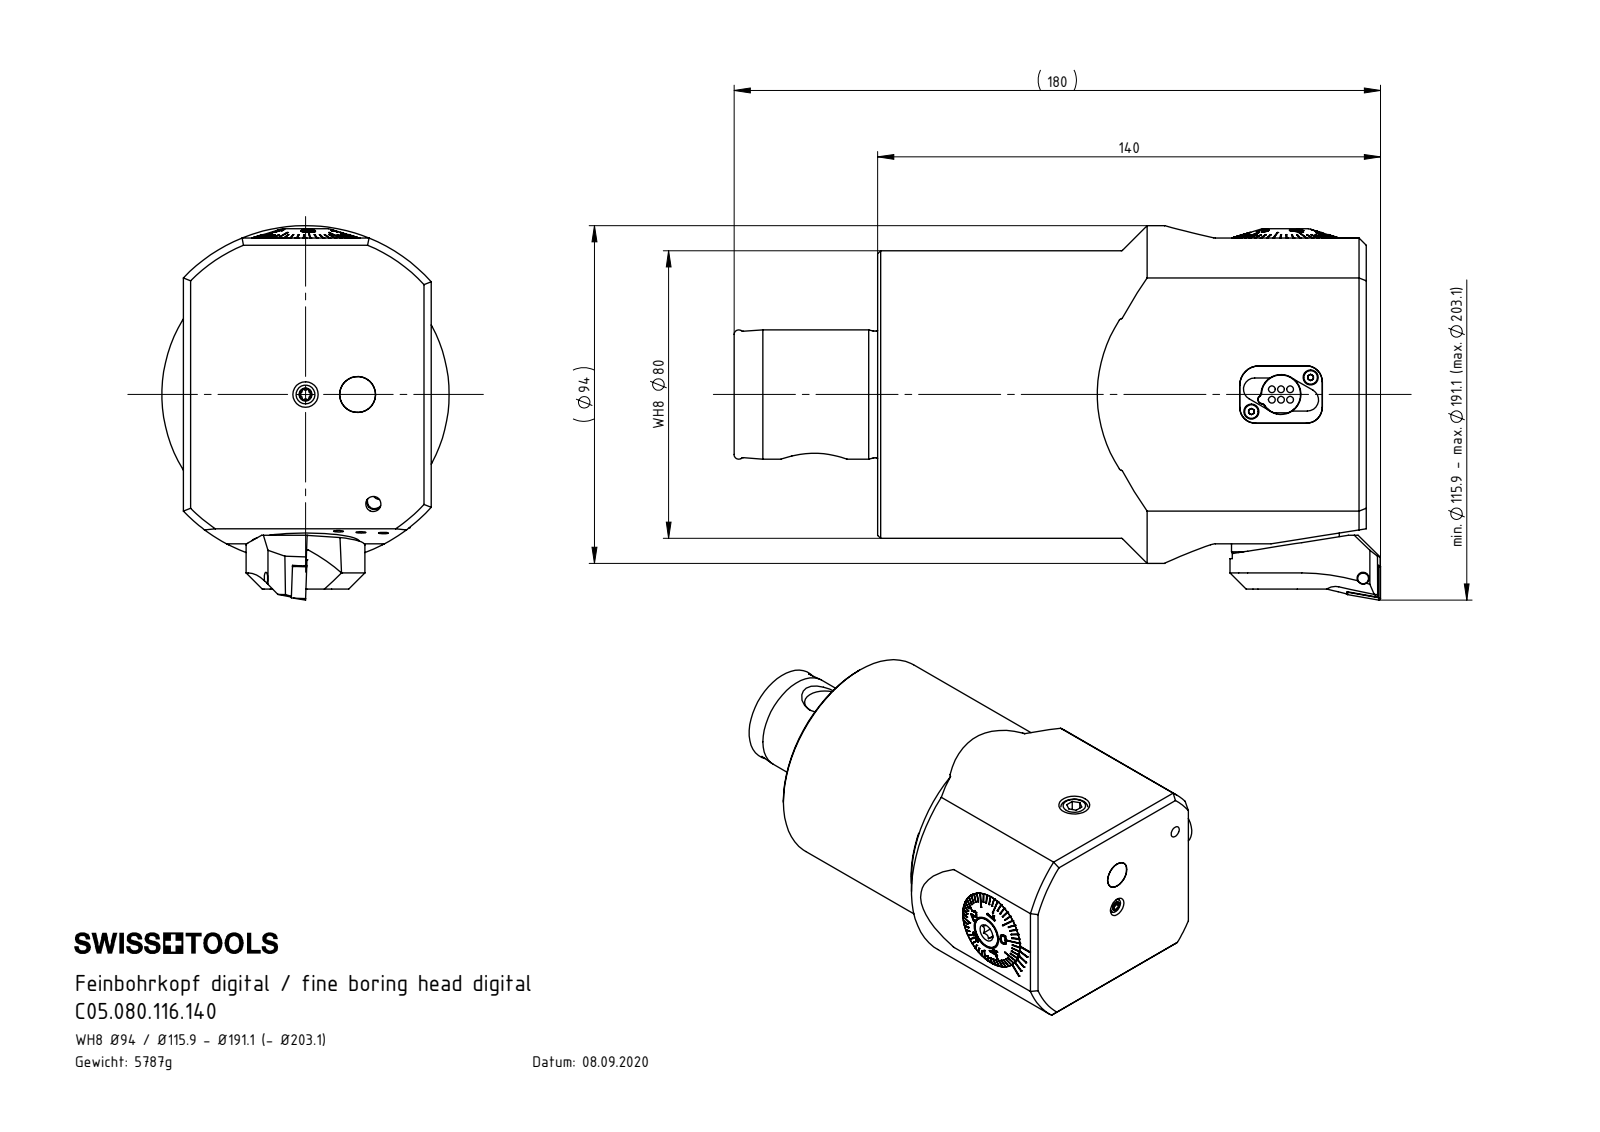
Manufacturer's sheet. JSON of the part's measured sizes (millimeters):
{"part_name": "Fxx-BG7.DA1.0xx_B_F72; WCB-ER2.001.009_A; Klebstoff D10; ISO 4026 - M10 x 16 (+8 more)", "step_written_by": "SolidWorks 2017 (CONFIG_CONTROL_DESIGN)", "units": "millimeters", "bodies": {"solids": 31, "faces": 1006, "planar": 469, "cylindrical": 219, "other": 318}, "overall_size": [176, 101.15, 80], "volume_mm3": 740095, "surface_area_mm2": 91312, "round_holes": [[4.2, 5], [2.5, 3], [1.6, 2], [2.2, 2], [3.3, 2], [8.5, 2], [13, 2], [5, 1], [8, 1], [9.5, 1], [10, 1], [10.2, 1]], "round_bosses_or_shafts": [[1.9, 6], [10, 2], [3.8, 2], [2, 2], [80, 1], [36, 1], [35.3, 1], [30, 1]], "partial_cylinders_radius": [[0.34, 6], [0.59, 6], [1.1, 6], [1.2, 6], [2, 6], [2.5, 6], [3.2, 3], [4.4, 3]], "face_to_face_distances": [69, 136, 6.5, 40, 176, 78.6, 85.1, 2.6, 87.7, 1.2], "hole_center_spacings": [9.52, 1.21, 8.49, 10.59, 14.5, 19.04]}
